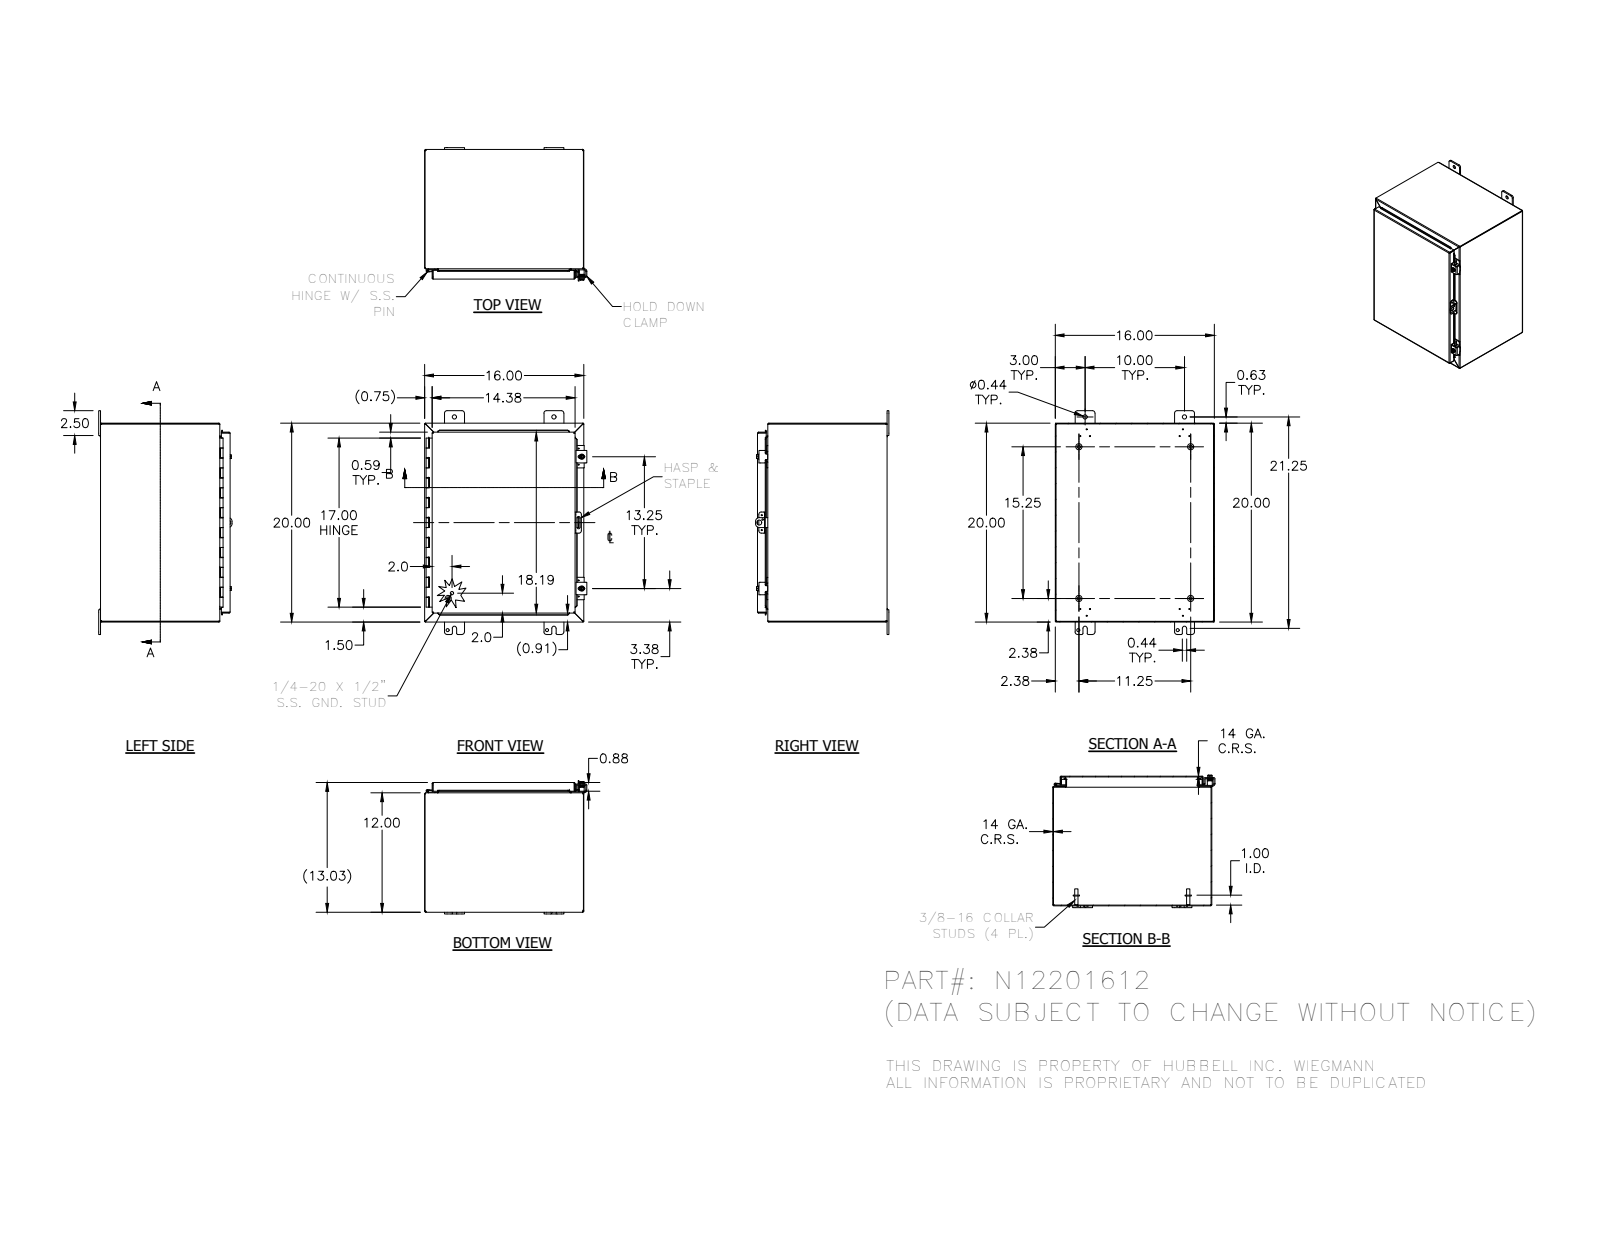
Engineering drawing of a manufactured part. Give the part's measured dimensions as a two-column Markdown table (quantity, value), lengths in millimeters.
| quantity | value |
| --- | --- |
| part name | N12201612; 34840; 38420; N12201612BKP (+8 more) |
| STEP written by | Autodesk Inventor 2012 (AUTOMOTIVE_DESIGN) |
| units | millimeters |
| bodies | 27 solids, 948 faces (511 planar, 320 cylindrical, 117 other) |
| overall size | 571.5 × 414.3 × 340.6 |
| volume | 2 219 000 mm³ |
| surface area | 2 285 000 mm² |
| round holes (diameter × count) | 3 × 12, 2.8 × 7, 8 × 4, 11.1 × 4, 5.4 × 2, 7.1 × 2, 7.6 × 2, 3.2 × 1, 4 × 1, 12.7 × 1 |
| round bosses / shafts (diameter × count) | 15.9 × 4, 8.4 × 4, 6.4 × 4, 13.2 × 2, 12.7 × 2, 8.9 × 2, 2.9 × 2, 8.6 × 1 |
| partial cylindrical surfaces (radius × count) | 0.8 × 27, 1.6 × 25, 3.2 × 25, 6.4 × 25, 0.8 × 23, 2.7 × 23, 1.8 × 8, 2.5 × 4 |
| main face-to-face distances | 1.9, 329.2, 404.5, 506.1, 327.3, 331, 402.6, 406.4, 508, 504.2 |
| hole center spacings | 254, 19.3, 21.3, 23.9, 24.6, 40.5, 50.7, 238.3 |
